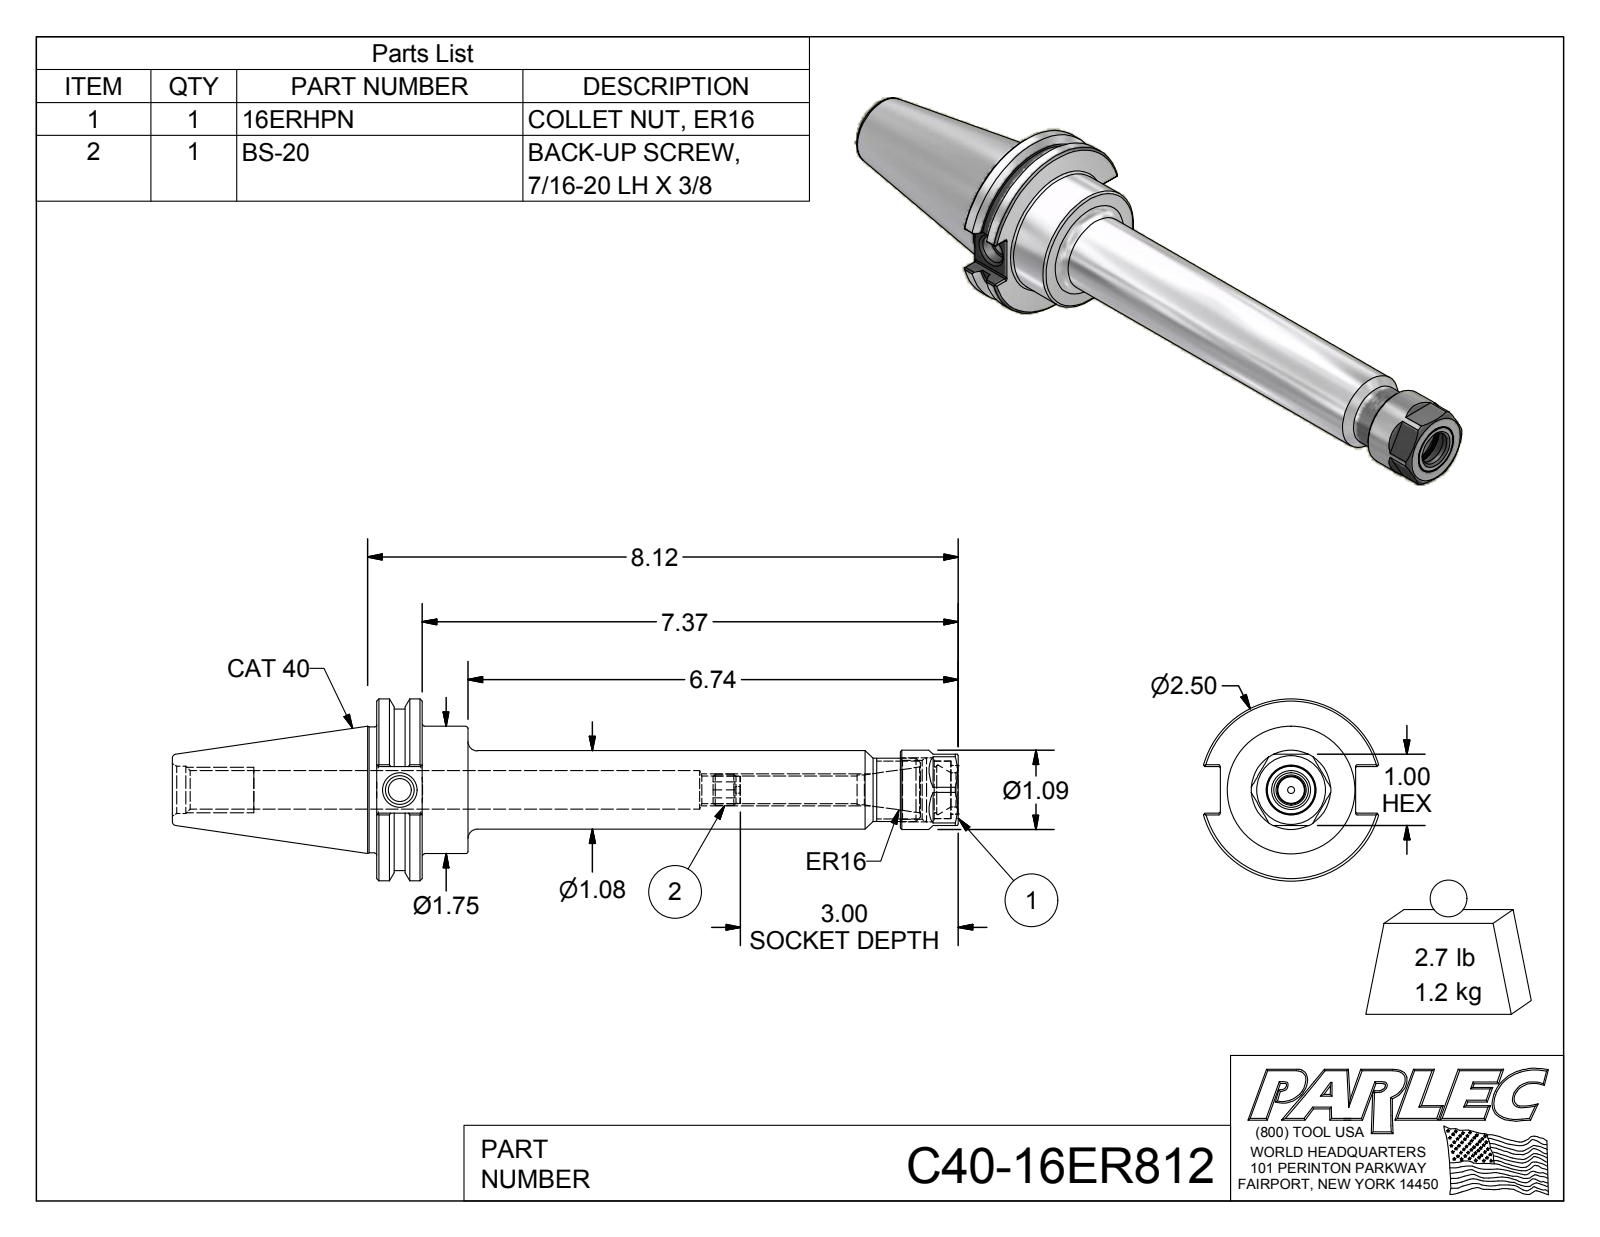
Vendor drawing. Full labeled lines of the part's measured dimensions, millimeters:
Part name (STEP PRODUCT): C40-16ER812; C40-16ER8-1; 16ERHPN; BS-20
STEP written by: Autodesk Inventor 2012 (AUTOMOTIVE_DESIGN)
Units: millimetres
Bodies: 4 solids, 145 faces (62 planar, 42 cylindrical, 41 other)
Overall size (bounding box): 274.5 × 63.5 × 61
Volume: 200 700 mm³ · Surface area: 47 520 mm²
Round holes (diameter × count): ⌀2.3 ×1, ⌀8 ×1, ⌀9.7 ×1, ⌀10.1 ×1, ⌀10.5 ×1, ⌀12 ×1, ⌀13.4 ×1, ⌀13.4 ×1, ⌀16 ×1, ⌀16.5 ×1, ⌀17.1 ×1, ⌀17.3 ×1
Round bosses / shafts (diameter × count): ⌀63.5 ×1, ⌀56.4 ×1, ⌀44.5 ×1, ⌀43.9 ×1, ⌀27.7 ×1, ⌀27.4 ×1, ⌀22 ×1, ⌀20.1 ×1
Partial cylindrical surfaces — rounded edges, fillets, slot ends (radius × count): R0.5 ×12
Main face-to-face distances: 15.9, 31.9, 16, 24.9, 203.1, 187.2, 171.2, 4.3, 20.6, 182.9
